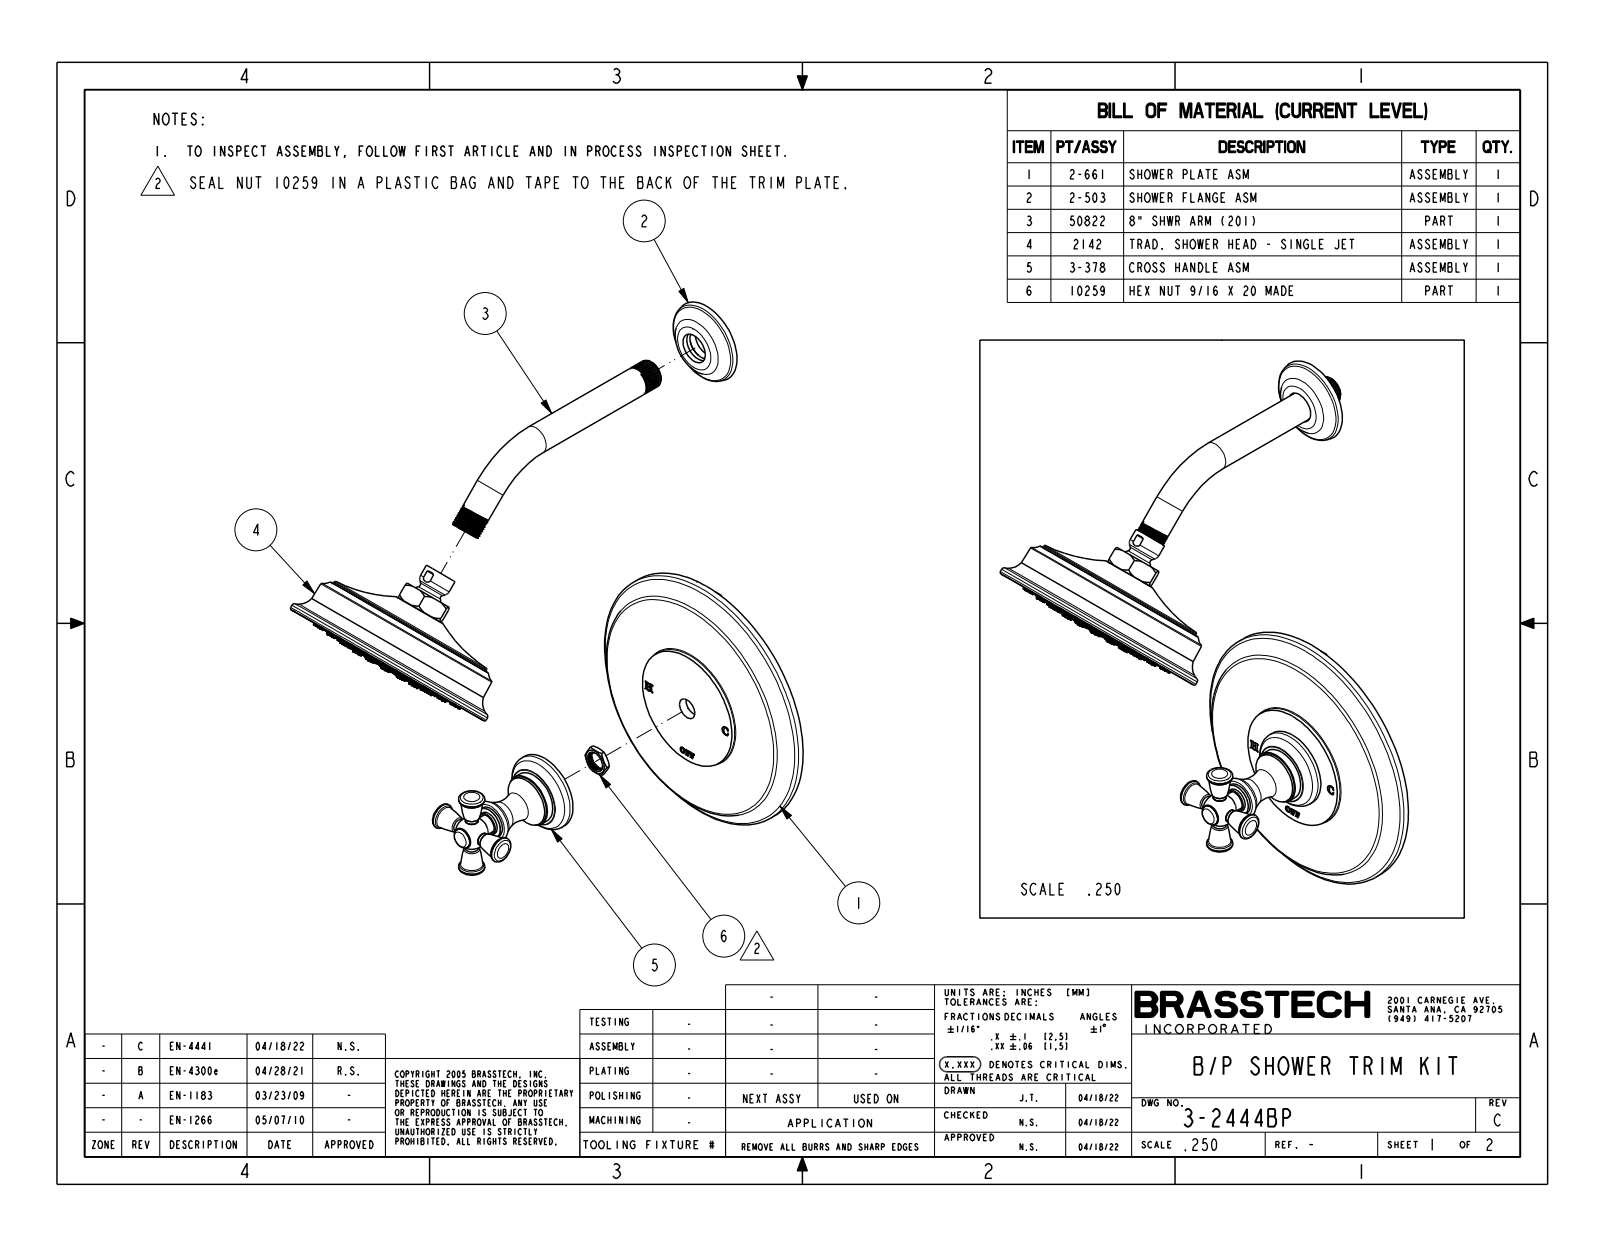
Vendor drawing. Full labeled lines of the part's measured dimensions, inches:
Part name (STEP PRODUCT): 3-2444BP
STEP written by: CREO PARAMETRIC BY PTC INC, 2018400 (CONFIG_CONTROL_DESIGN)
Units: inches
Bodies: 2 solids, 1286 faces (272 planar, 246 cylindrical, 768 other)
Overall size (bounding box): 16.935 × 10.691 × 7.5
Volume: 69.79 in³ · Surface area: 233.5 in²
Round holes (diameter × count): ⌀0.05 ×90, ⌀0.22 ×1, ⌀0.604 ×1, ⌀5.275 ×1
Round bosses / shafts (diameter × count): ⌀1.42 ×2, ⌀0.813 ×2, ⌀0.72 ×2, ⌀0.36 ×2, ⌀7.5 ×1, ⌀6.2 ×1, ⌀5.22 ×1, ⌀4.83 ×1
Main face-to-face distances: 0.625, 0.125, 0.75, 0.48, 0.145, 0.27, 1.014, 1.011, 2.025, 2.986
Hole centre spacings: 0.48, 1.84, 1.84, 2.27, 0.952, 1.408, 0.474, 2.24
